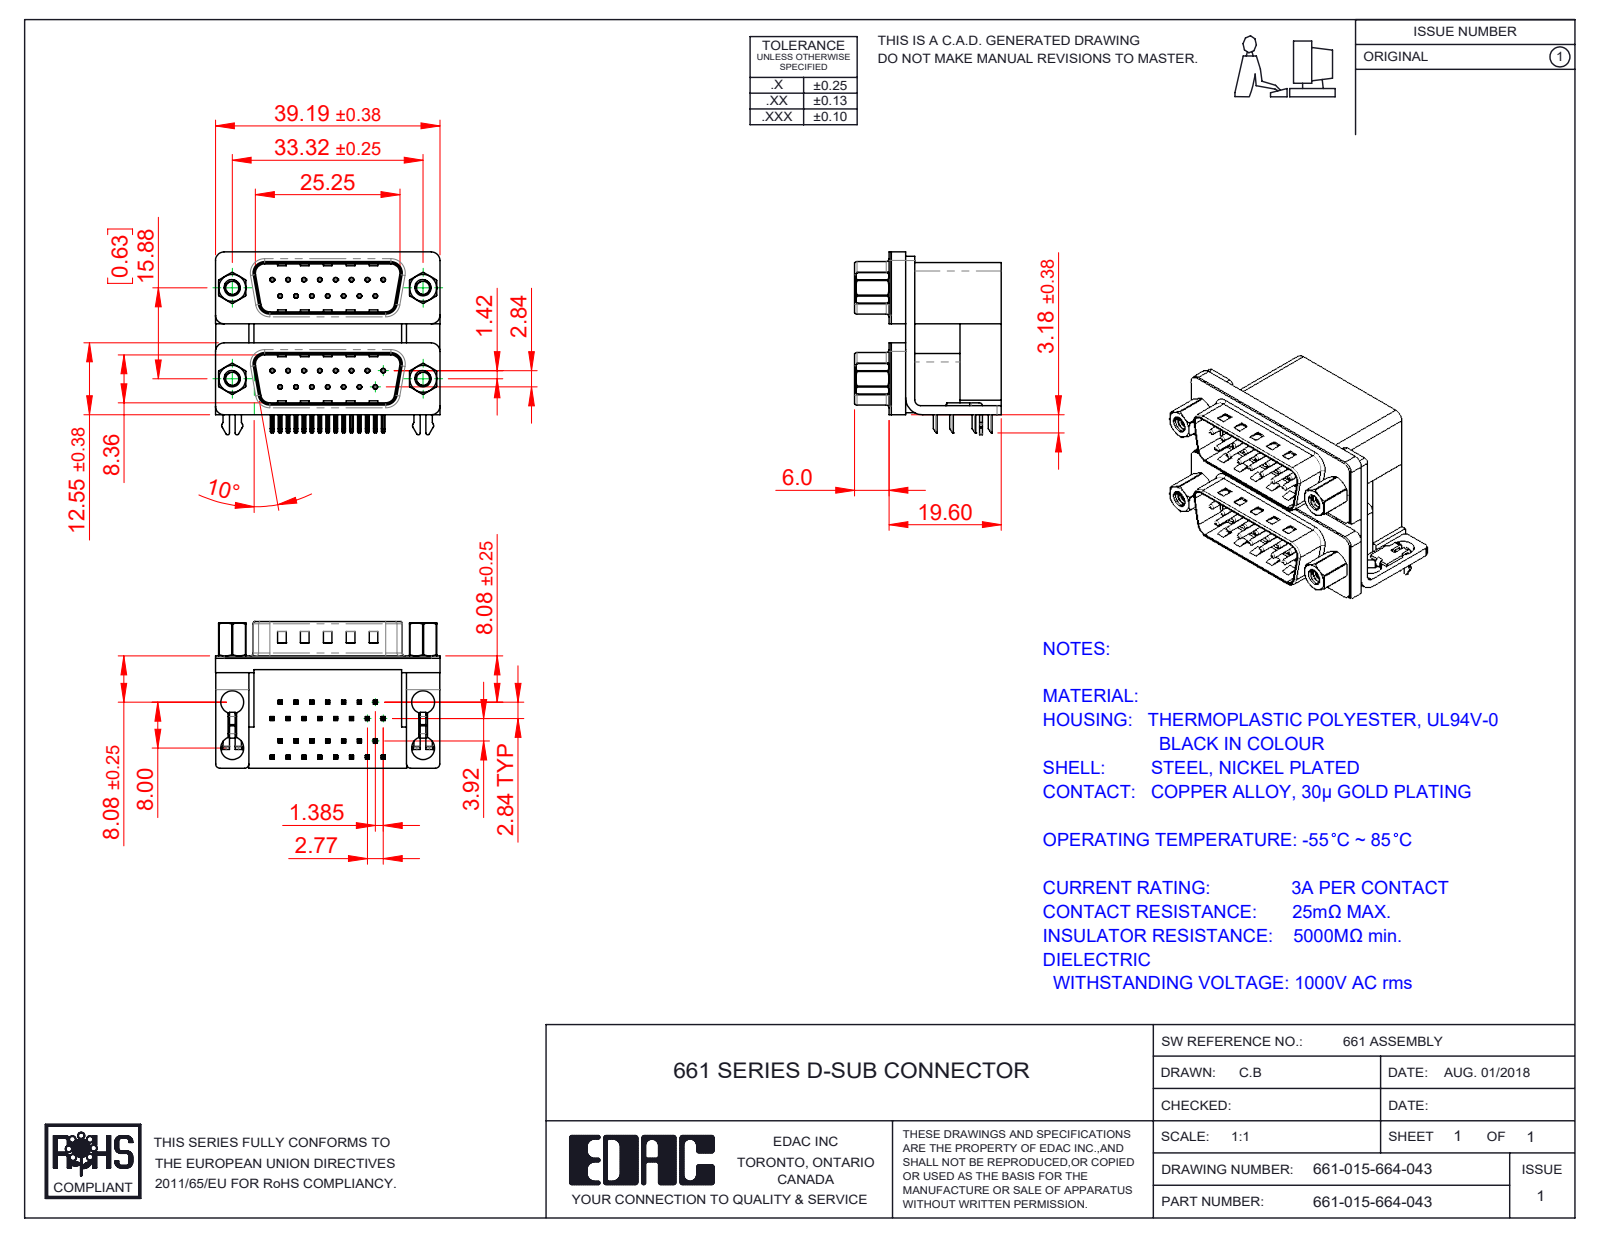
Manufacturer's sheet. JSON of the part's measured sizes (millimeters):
{"part_name": "661 Contact Bottom Upper_L; 661 Contact Bottom Lower; 661-015-664-043; 661 2 Prong Board Lock_4 (+8 more)", "step_written_by": "SolidWorks 2020 (CONFIG_CONTROL_DESIGN)", "units": "millimeters", "bodies": {"solids": 47, "faces": 3322, "planar": 1956, "cylindrical": 1028, "other": 338}, "overall_size": [39.19, 31.93, 25.6], "volume_mm3": 14170, "surface_area_mm2": 16195, "round_holes": [[0.35, 30], [0.8, 30], [4, 8], [2.26, 4], [2.29, 4], [3.5, 4], [4.8, 4], [5, 4]], "round_bosses_or_shafts": [[0.75, 30], [4.9, 4], [4.75, 4], [3.9, 4], [2.79, 4]], "partial_cylinders_radius": [[0.25, 126], [0.12, 60], [0.5, 20], [1.5, 16], [0.75, 10], [0.9, 8], [1.6, 8], [2, 8]], "face_to_face_distances": [0.4, 19.2, 16.7, 2.5, 15.87, 7.2, 12, 9.5, 10.7, 2.9], "hole_center_spacings": [3.16, 2.77, 16.12, 5.54, 16.82, 8.31, 17.92, 15.88]}
